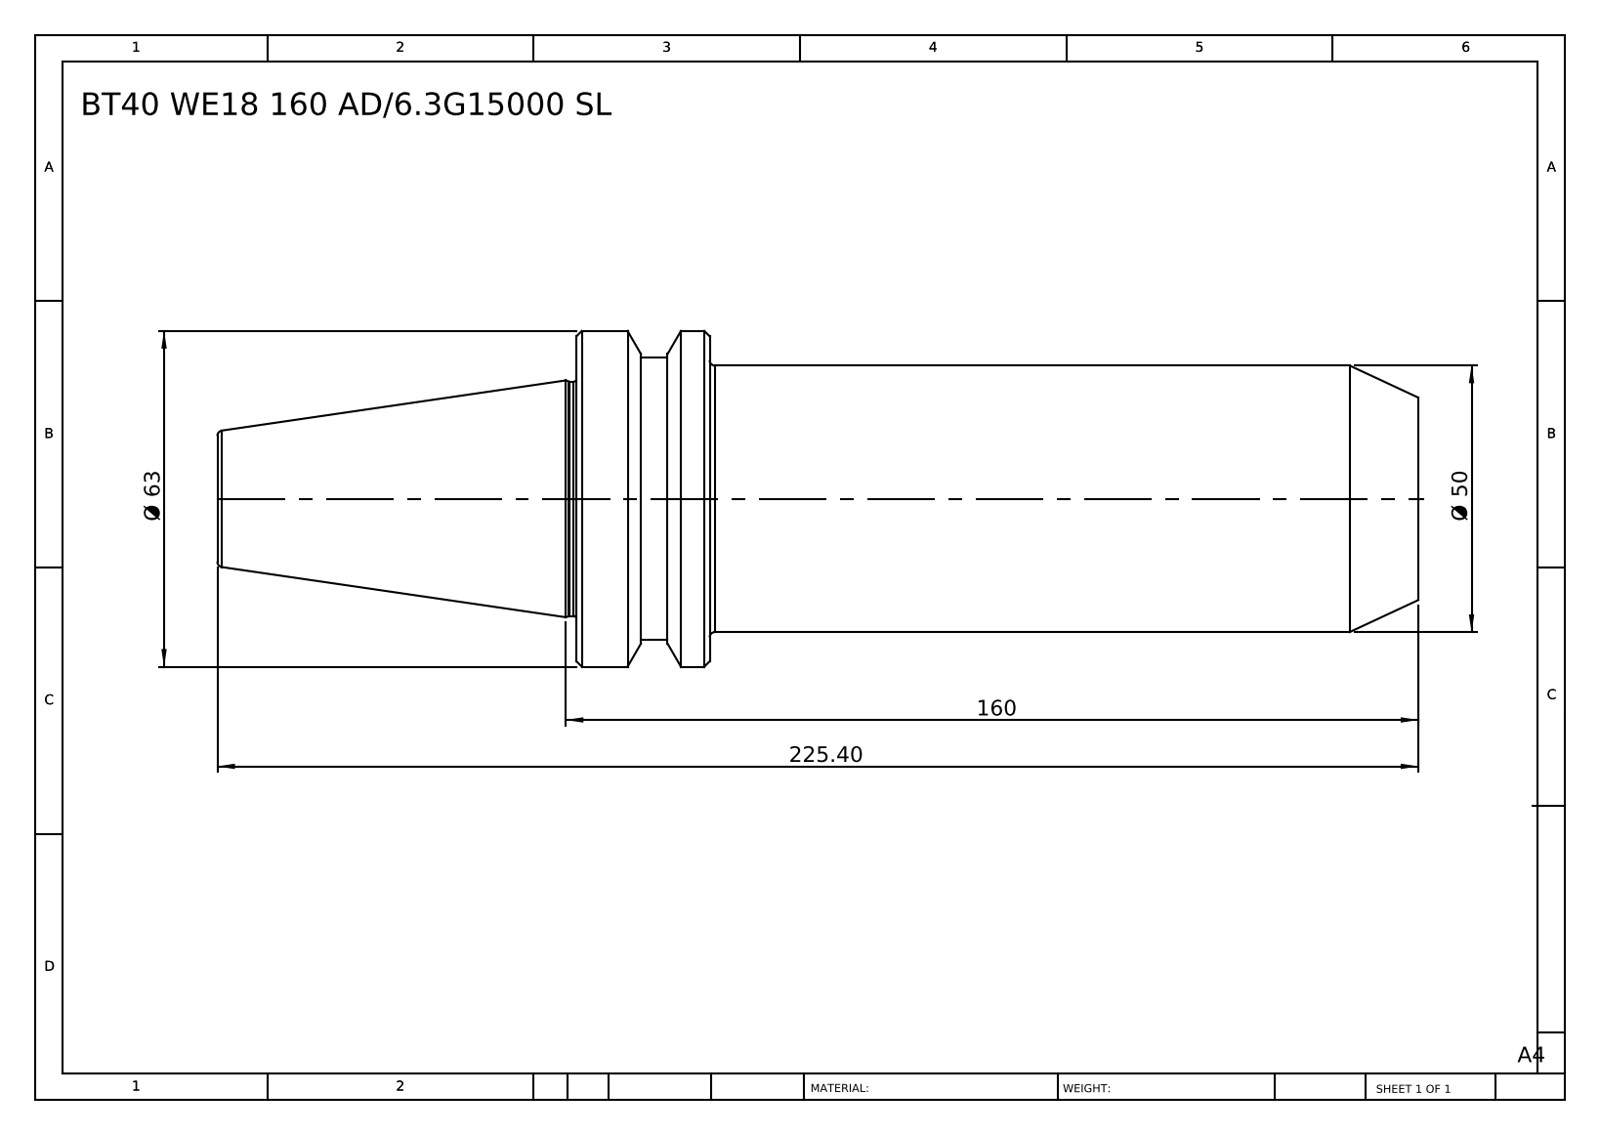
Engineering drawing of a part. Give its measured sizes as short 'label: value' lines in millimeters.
name: BT40 WE18 160 AD-6.3G15000 SL
written by: SolidWorks 2014 (CONFIG_CONTROL_DESIGN)
unit: mm
bodies: 1 solid, 38 faces (6 planar, 10 cylindrical, 22 other)
size: 225.4 × 63 × 63
volume: 393 947 mm³; area: 38 269 mm²
bosses: 1× ⌀63, 1× ⌀53, 1× ⌀50, 1× ⌀44
face distances: 158, 133, 25, 225.4, 92.4, 67.4, 145.9, 12.9, 12.1, 79.5
